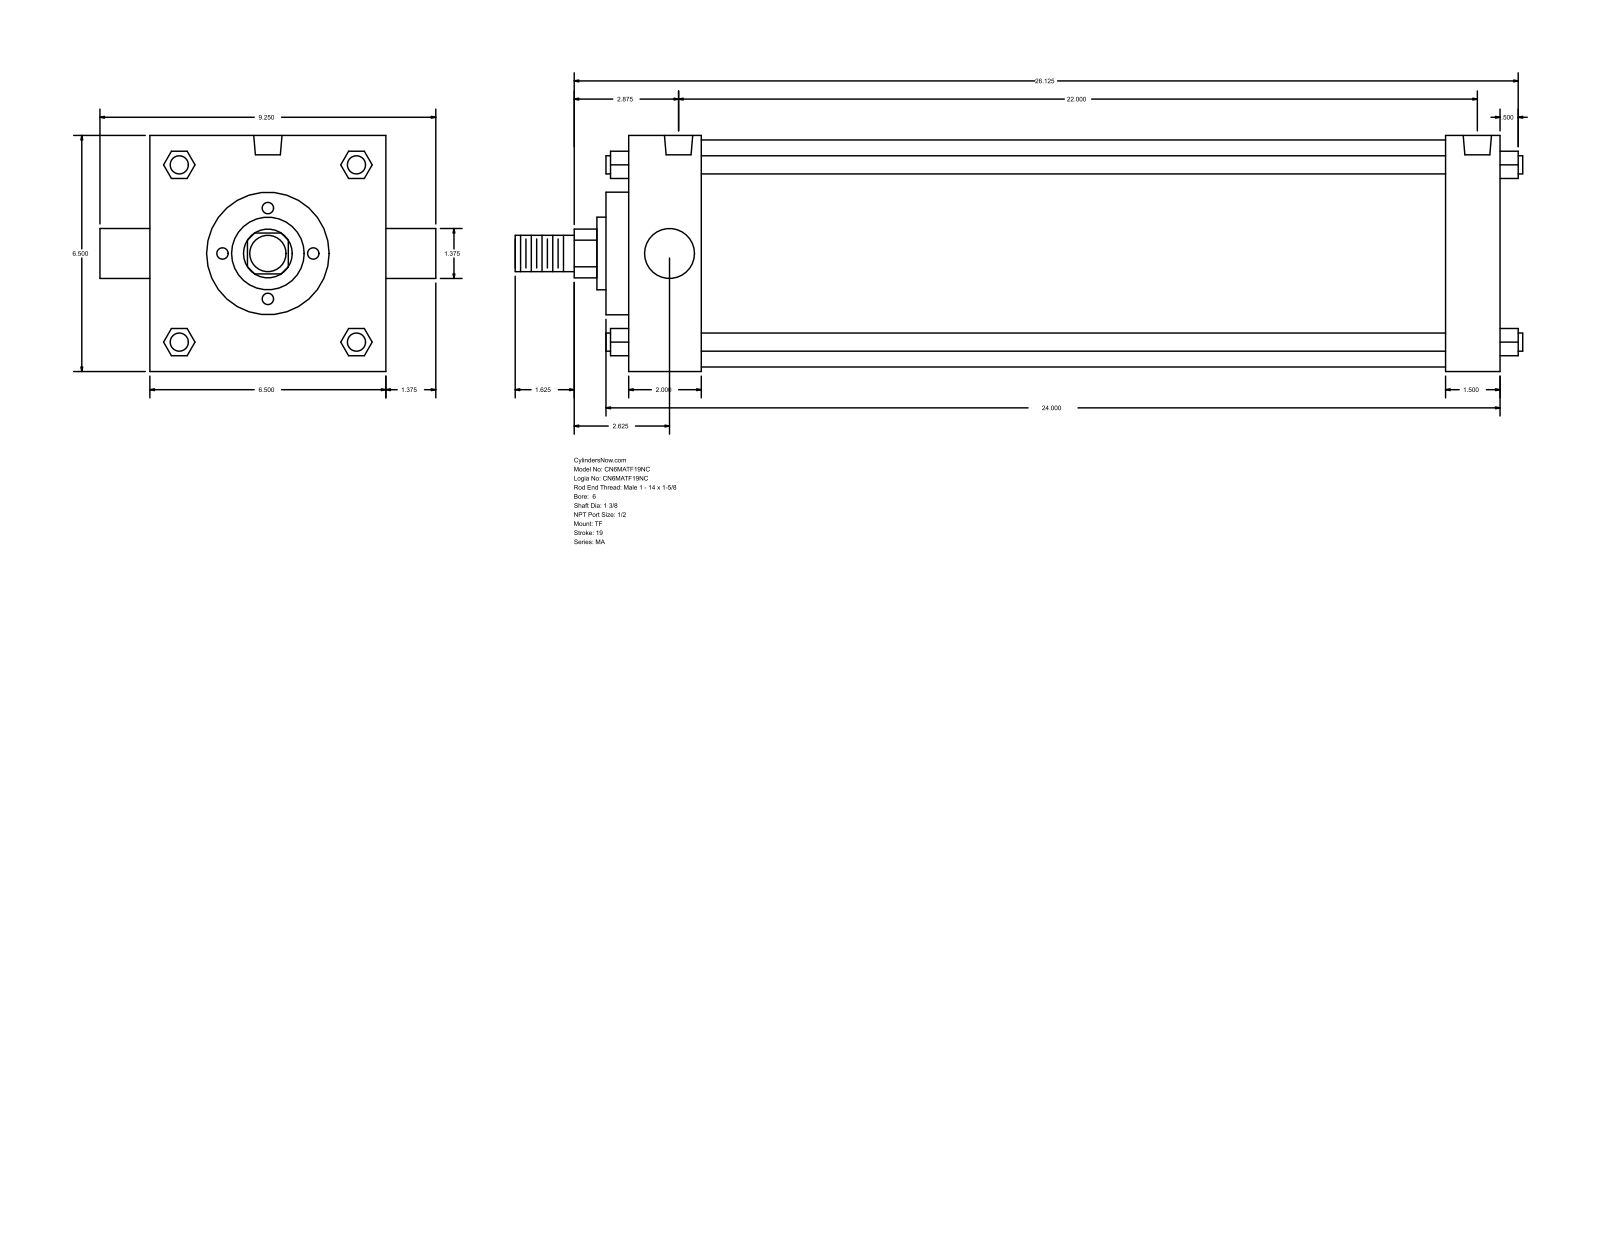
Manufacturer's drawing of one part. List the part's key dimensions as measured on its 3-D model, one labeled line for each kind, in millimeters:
Part name (STEP PRODUCT): MA_TF__0600_1.375
STEP written by: GSSL Pune (CONFIG_CONTROL_DESIGN)
Units: millimetres
Bodies: 0 solids, 122 faces (93 planar, 29 cylindrical, 0 other)
Overall size (bounding box): 704.85 × 234.95 × 165.1
Round holes (diameter × count): ⌀17.46 ×3, ⌀19.77 ×2
Round bosses / shafts (diameter × count): ⌀12.7 ×4, ⌀34.92 ×2, ⌀158.75 ×1, ⌀85.72 ×1, ⌀50.8 ×1, ⌀25.4 ×1
Partial cylindrical surfaces — rounded edges, fillets, slot ends (radius × count): R17.06 ×1
Main face-to-face distances: 165.1, 612.78, 50.8, 561.98, 574.67, 523.87, 38.11, 66.67, 15.87, 590.54
Hole centre spacings: 3.18, 558.8, 561.98
